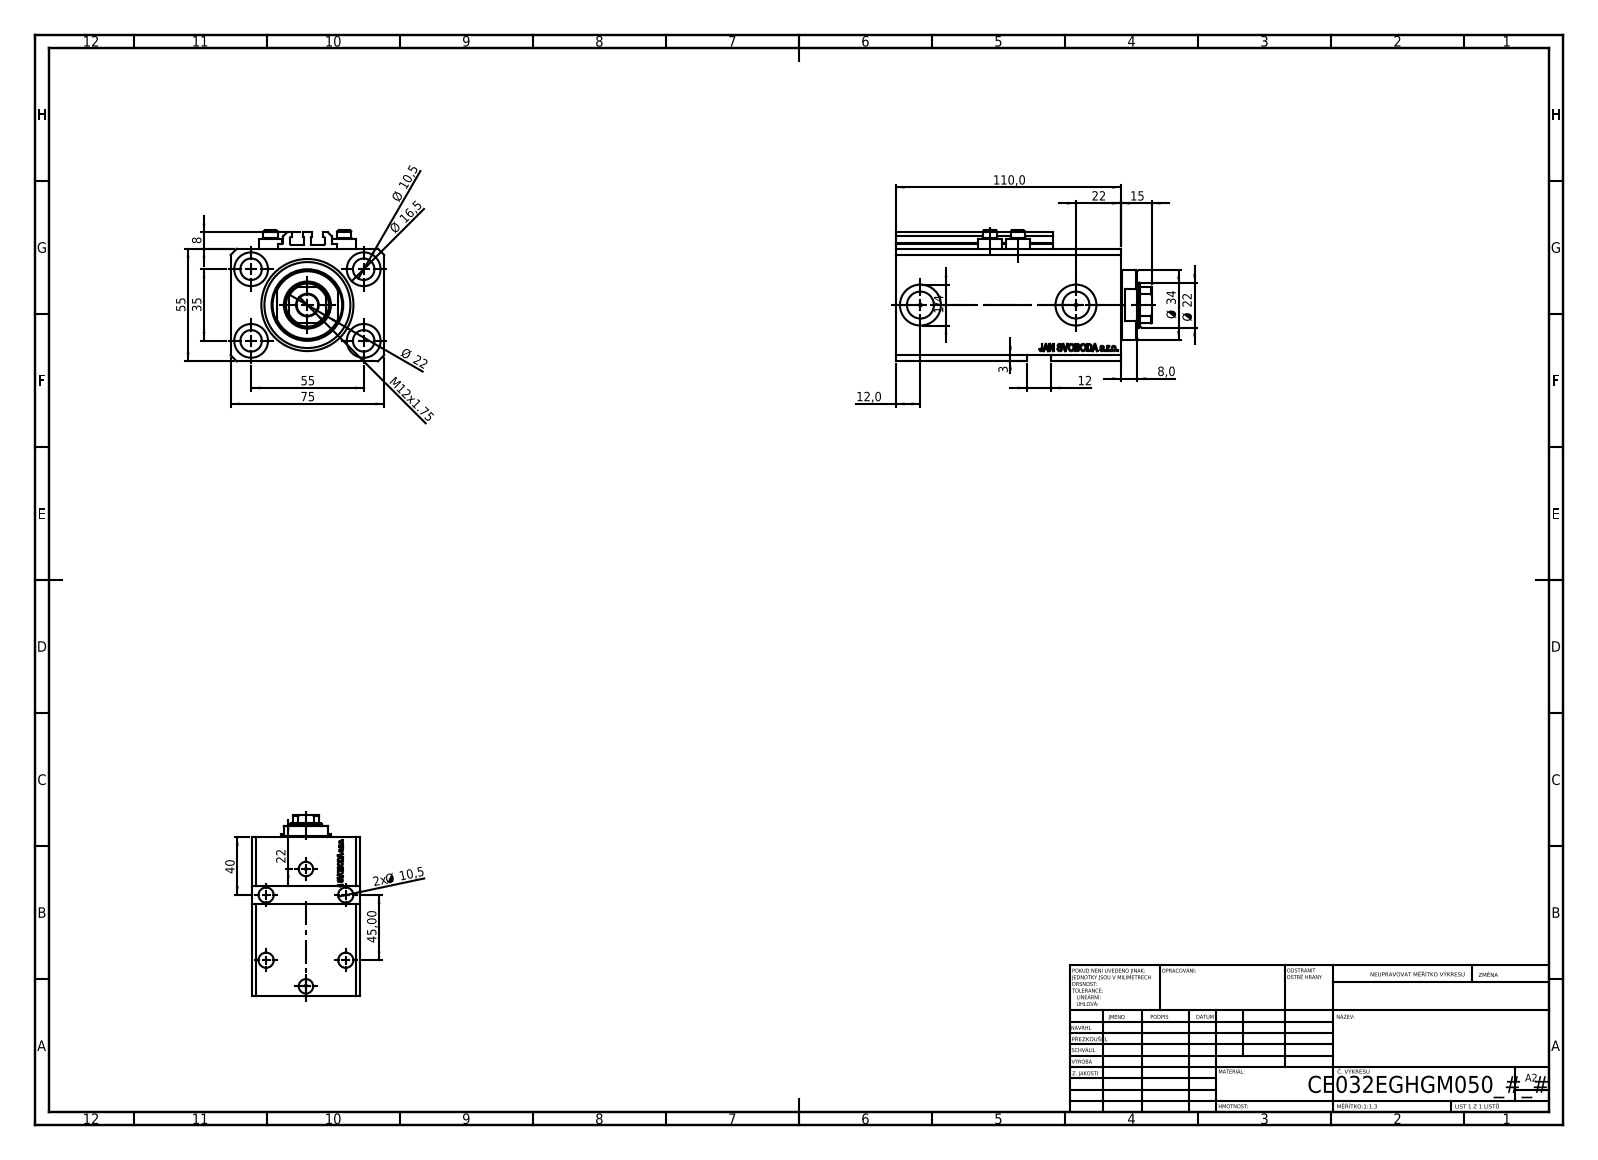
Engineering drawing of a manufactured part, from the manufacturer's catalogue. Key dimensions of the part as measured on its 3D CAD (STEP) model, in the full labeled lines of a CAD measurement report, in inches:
Part name (STEP PRODUCT): ALLEN BOLT V250CE; V250CE_VC_E; V250CE_C_VCP; V250CE_E_Body
STEP written by: SolidWorks 2019 (CONFIG_CONTROL_DESIGN)
Units: inches
Bodies: 8 solids, 1084 faces (514 planar, 146 cylindrical, 424 other)
Overall size (bounding box): 4.921 × 2.953 × 2.52
Volume: 23.27 in³ · Surface area: 148.2 in²
Round holes (diameter × count): ⌀0.413 ×9, ⌀0.049 ×4, ⌀0.157 ×4, ⌀0.65 ×4, ⌀0.394 ×2, ⌀0.518 ×2, ⌀0.787 ×2, ⌀0.866 ×1, ⌀1.26 ×1, ⌀1.772 ×1
Round bosses / shafts (diameter × count): ⌀0.457 ×4, ⌀0.276 ×4, ⌀1.339 ×1
Partial cylindrical surfaces — rounded edges, fillets, slot ends (radius × count): R0.008 ×10, R0.413 ×1
Main face-to-face distances: 2.165, 2.953, 0.591, 4.331, 3.74, 0.118, 0.39, 3.35, 3.941, 2.244
Hole centre spacings: 1.283, 1.294, 2.165, 2.706, 0.535, 0.555, 0.907, 1.016
